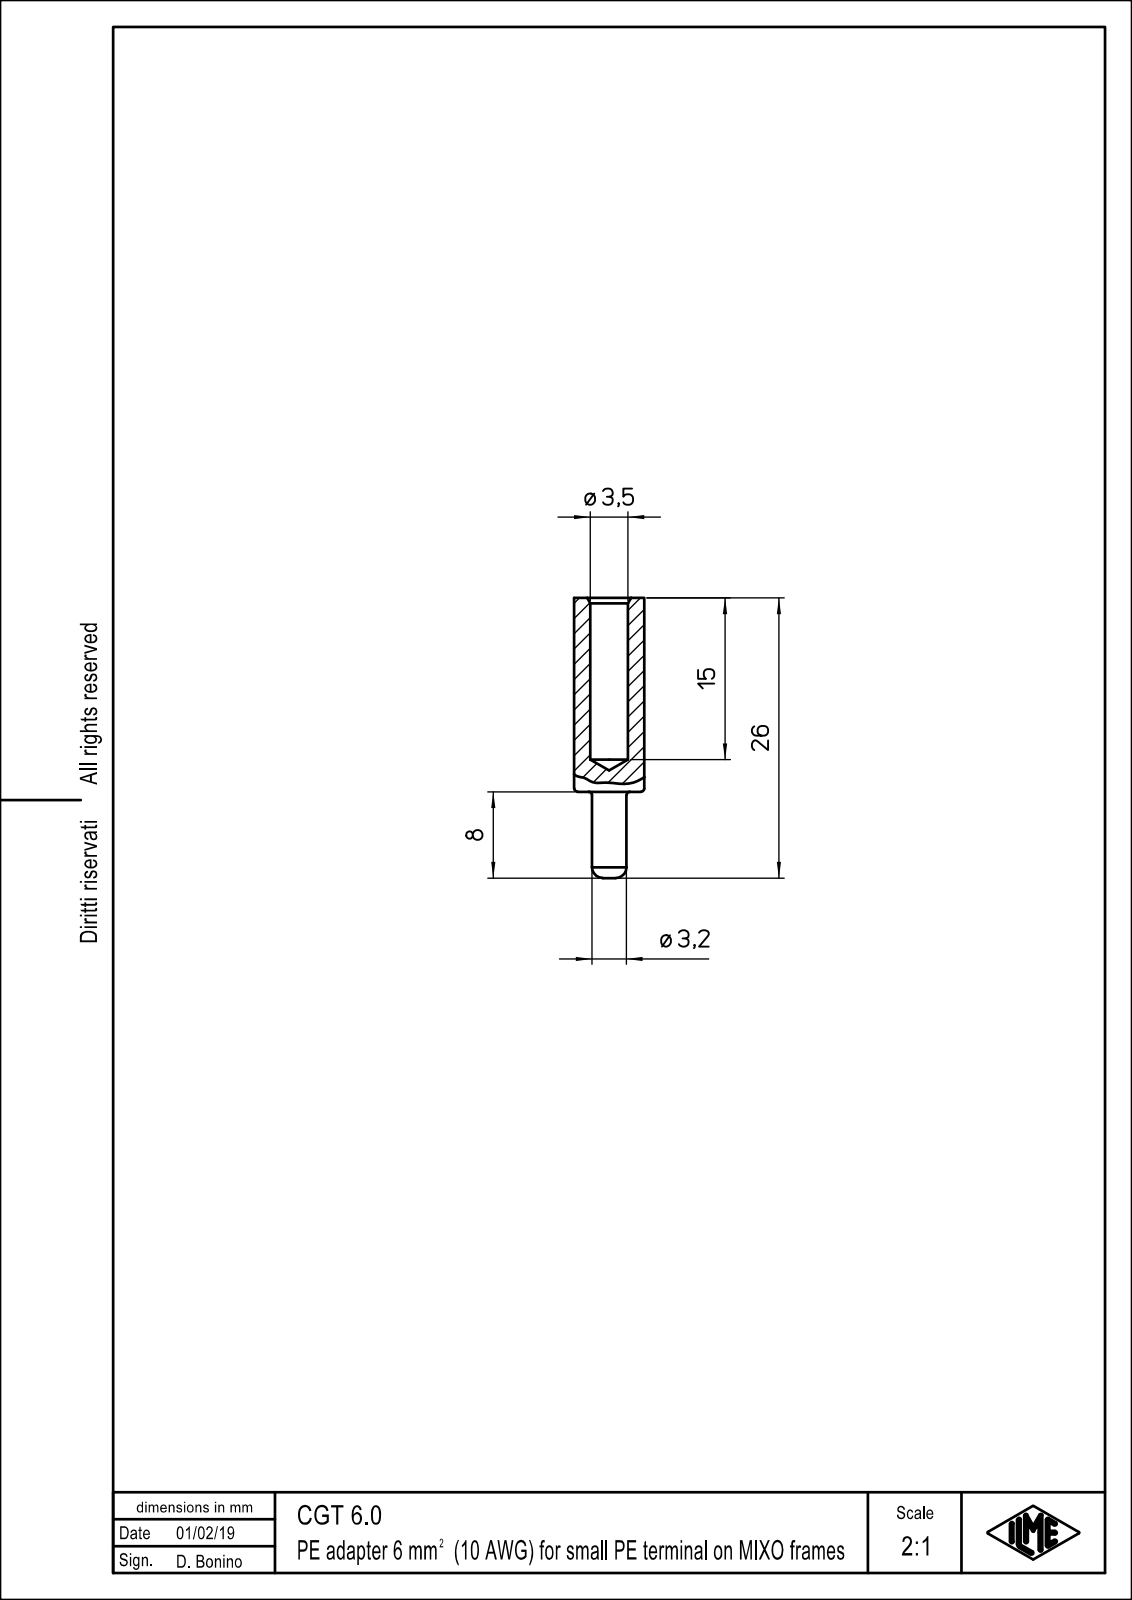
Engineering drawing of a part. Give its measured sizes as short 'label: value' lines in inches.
name: CGT_6.0
written by: PTC Creo Elements/Direct Modeling 19.0B 21-Mar-2015 (C) Parametric Technology GmbH (AUTOMOTIVE_DESIGN)
unit: in
bodies: 1 solid, 19 faces (3 planar, 6 cylindrical, 10 other)
size: 1.024 × 0.256 × 0.256
volume: 0.031 in³; area: 1.04 in²
holes: 1× ⌀0.138
bosses: 1× ⌀0.256, 1× ⌀0.126
face distances: 0.709, 1.024, 0.315
